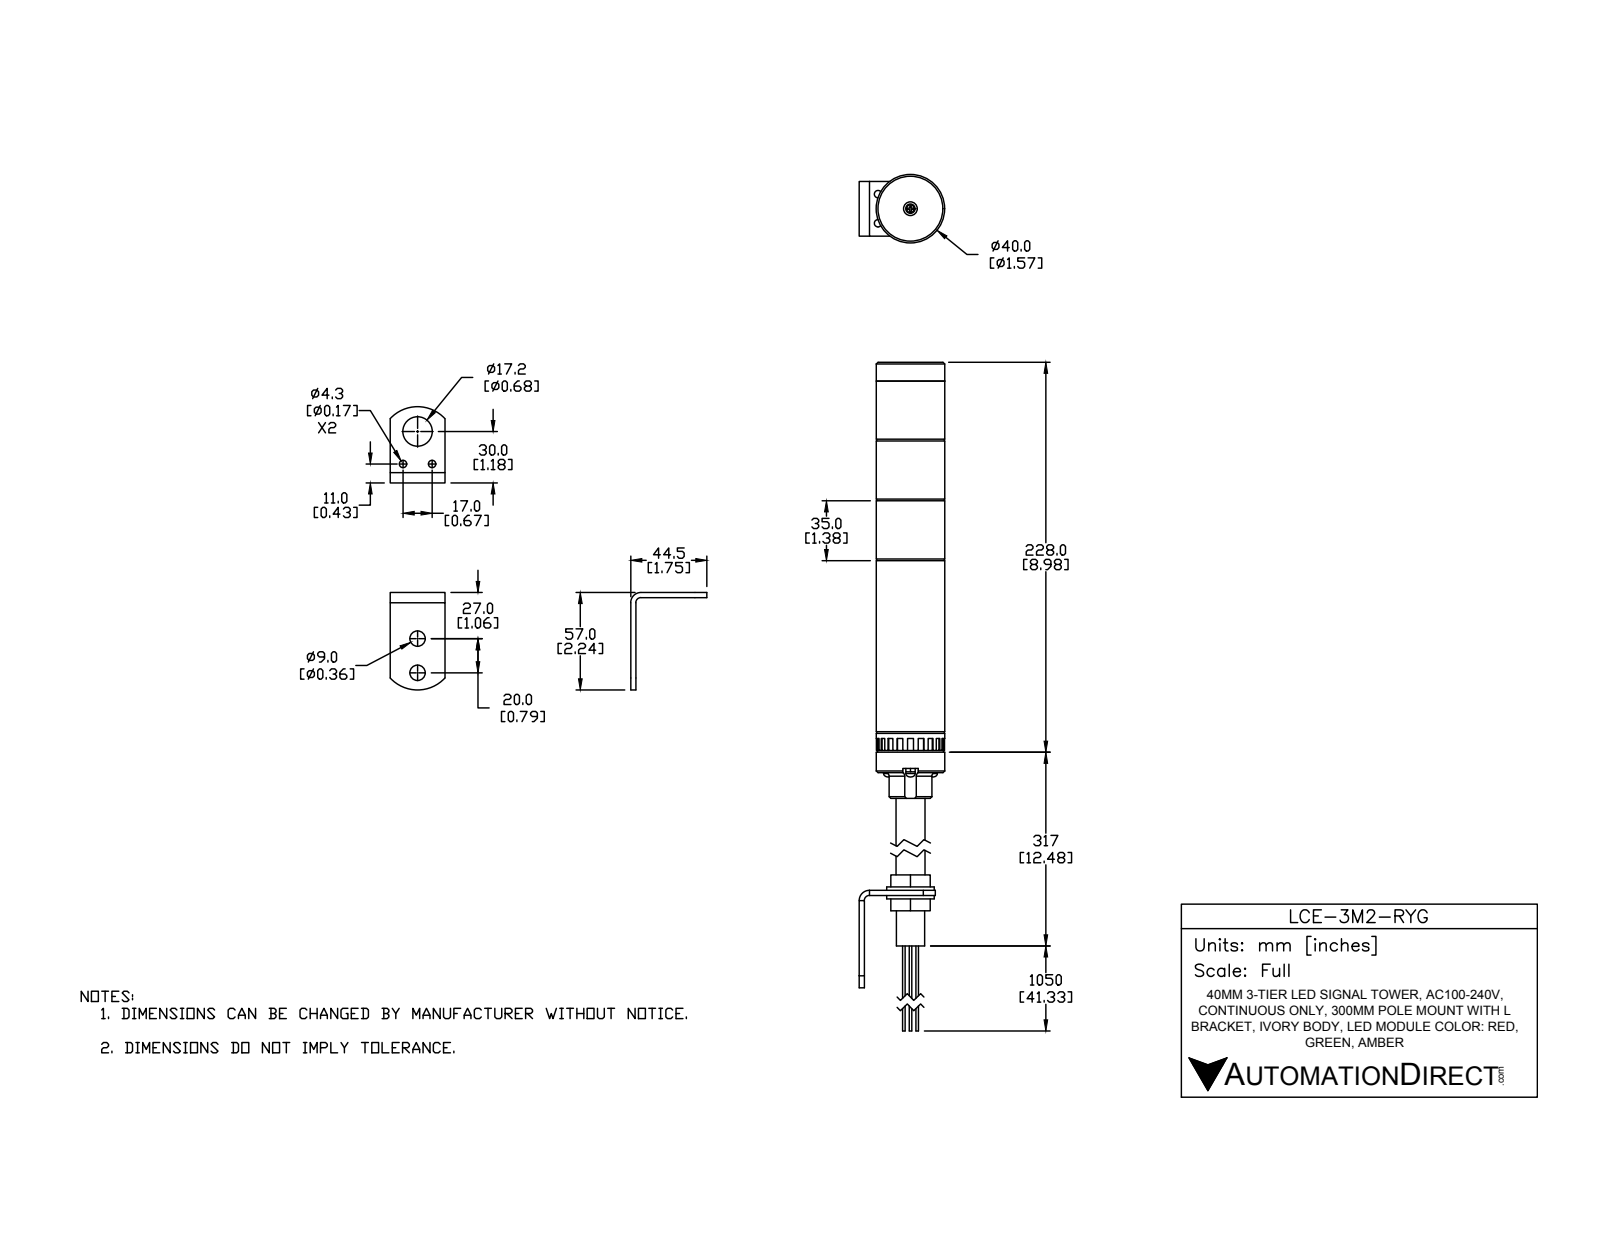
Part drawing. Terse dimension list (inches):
name: LCE-3M2-RYG
written by: SolidWorks 2016 (AUTOMOTIVE_DESIGN)
unit: in
bodies: 34 solids, 381 faces (243 planar, 118 cylindrical, 20 other)
size: 25.433 × 1.969 × 1.575
volume: 22.01 in³; area: 196.6 in²
holes: 3× ⌀0.138, 3× ⌀0.157, 2× ⌀0.169, 2× ⌀0.356, 1× ⌀0.315, 1× ⌀0.472, 1× ⌀0.677, 1× ⌀0.689, 1× ⌀0.709
bosses: 6× ⌀0.118, 6× ⌀0.059, 4× ⌀0.217, 1× ⌀1.575, 1× ⌀1.555, 1× ⌀1.516, 1× ⌀1.094, 1× ⌀0.669
rounds: 3× R0.177, 2× R0.858, 1× R0.118, 1× R0.236, 1× R0.492
face distances: 1.378, 0.039, 2.756, 1.339, 0.433, 1.417, 2.717, 3.976, 5.354, 6.732
hole spacings: 0.591, 1.023, 0.819, 0.24, 0.669, 0.673, 0.787, 0.791
